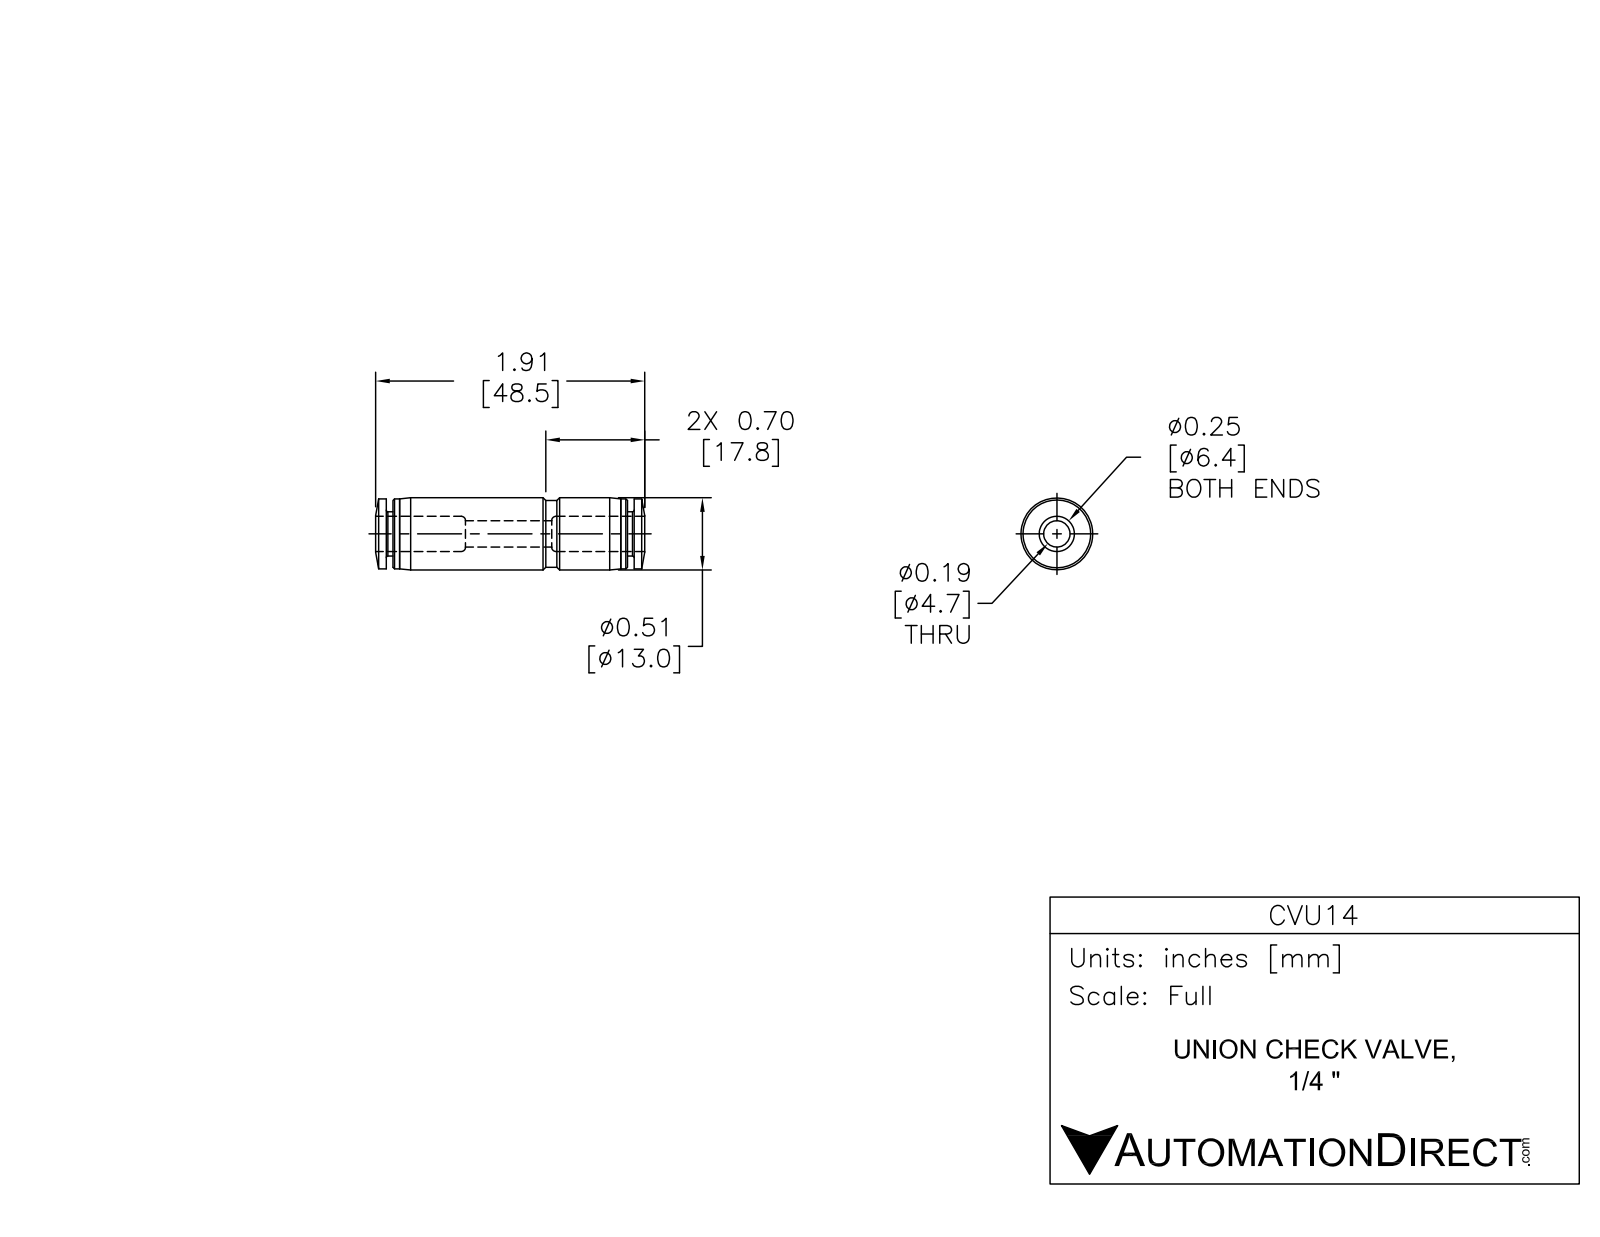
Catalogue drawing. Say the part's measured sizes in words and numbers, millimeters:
The part is named "CVU14". Its 3-D file was written by "SolidWorks 2015 (AUTOMOTIVE_DESIGN)". It is 1 solid with 84 faces: 20 planar, 32 cylindrical and 32 other. Overall it measures 48.4 by 13 by 13 millimeters. Its volume is 4 640 cubic millimeters and its surface area 3 309 square millimeters. Round holes: 1 of diameter 5.1, 1 of diameter 6.6. Round bosses or shafts: 1 of diameter 13, 1 of diameter 12.6, 1 of diameter 12, 1 of diameter 8, 1 of diameter 2.8. Partial cylindrical surfaces (rounded edges, fillets, slot ends): 1 of radius 1.8, 1 of radius 6.4. The main face-to-face distances are 1.2, 43.4, 44.6, 42.2, 14.9, 29.7, 13.7, 28.5, 14.8, 0.4.
